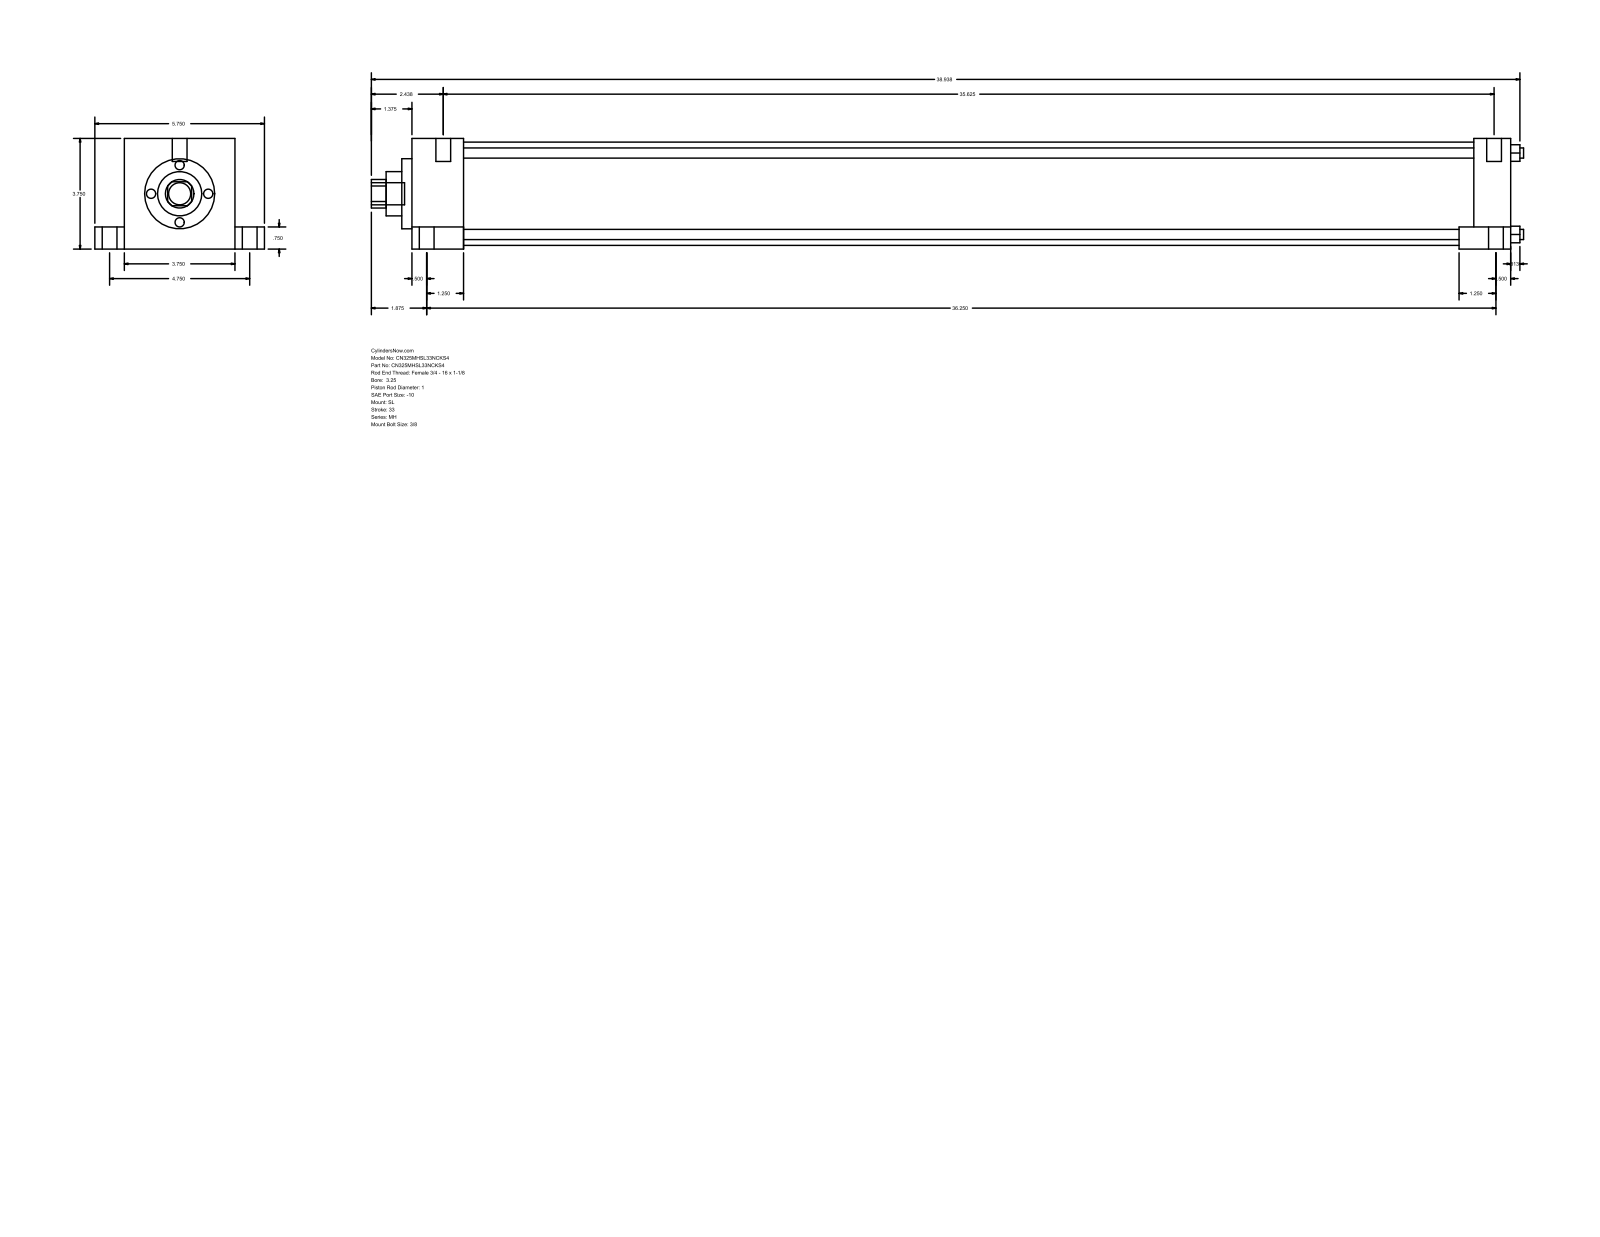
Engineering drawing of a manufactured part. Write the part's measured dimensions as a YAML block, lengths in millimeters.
part_name: "MH_SL__0325_1"
step_written_by: "GSSL Pune (CONFIG_CONTROL_DESIGN)"
units: millimeters
bodies: {solids: 0, faces: 110, planar: 77, cylindrical: 33, other: 0}
overall_size: [992.19, 146.05, 95.25]
round_holes:
  - {diameter: 8.76, count: 4}
  - {diameter: 25.4, count: 1}
  - {diameter: 38.1, count: 1}
  - {diameter: 60.33, count: 1}
  - {diameter: 88.9, count: 1}
round_bosses_or_shafts:
  - {diameter: 12.7, count: 6}
  - {diameter: 19.05, count: 5}
  - {diameter: 5.56, count: 4}
partial_cylinders:
  - {radius: 12.29, count: 1}
face_to_face_distances: [95.24, 946.16, 44.46, 901.7, 25.41, 120.65, 19.05, 76.19, 914.41, 869.95]
hole_center_spacings: [49.57, 70.1, 99.14]
